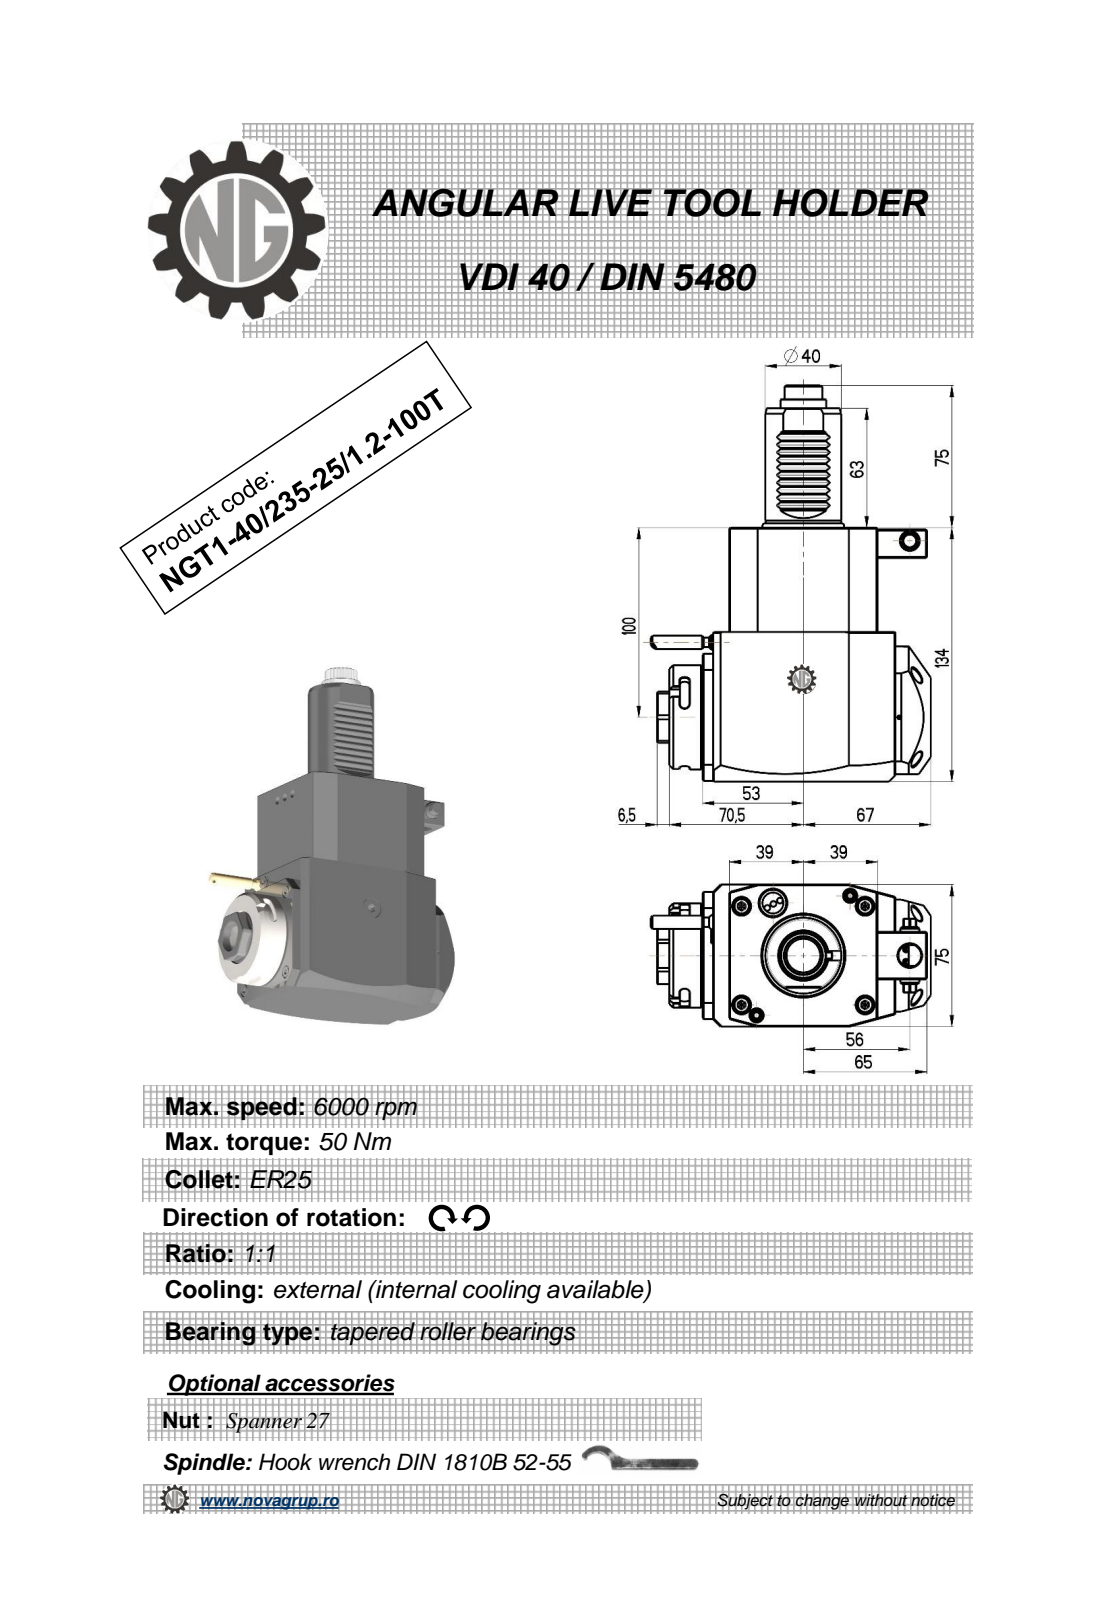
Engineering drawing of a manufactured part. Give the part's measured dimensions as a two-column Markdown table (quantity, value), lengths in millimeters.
| quantity | value |
| --- | --- |
| part name | NGT1_40_235_25_1_2_100T |
| STEP written by | PRO/ENGINEER BY PARAMETRIC TECHNOLOGY CORPORATION, 2010280 (CONFIG_CONTROL_DESIGN) |
| units | millimeters |
| bodies | 1 solid, 458 faces (186 planar, 178 cylindrical, 94 other) |
| overall size | 209 × 147.33 × 75 |
| volume | 1 074 000 mm³ |
| surface area | 76 992 mm² |
| round holes (diameter × count) | 2.5 × 1, 3 × 1, 9.5 × 1, 12 × 1, 18 × 1 |
| round bosses / shafts (diameter × count) | 8 × 2, 55 × 1, 48 × 1, 40 × 1, 24 × 1, 10 × 1, 7 × 1, 5 × 1 |
| partial cylindrical surfaces (radius × count) | 2.08 × 48, 0.3 × 10, 2.5 × 6, 15 × 2, 180 × 2, 3.85 × 1, 4.25 × 1, 9.08 × 1 |
| main face-to-face distances | 75, 134, 78, 14, 92, 17.5, 31.5, 79, 84.88, 109.5 |
| hole center spacings | 43.2, 54.87, 91.5 |
